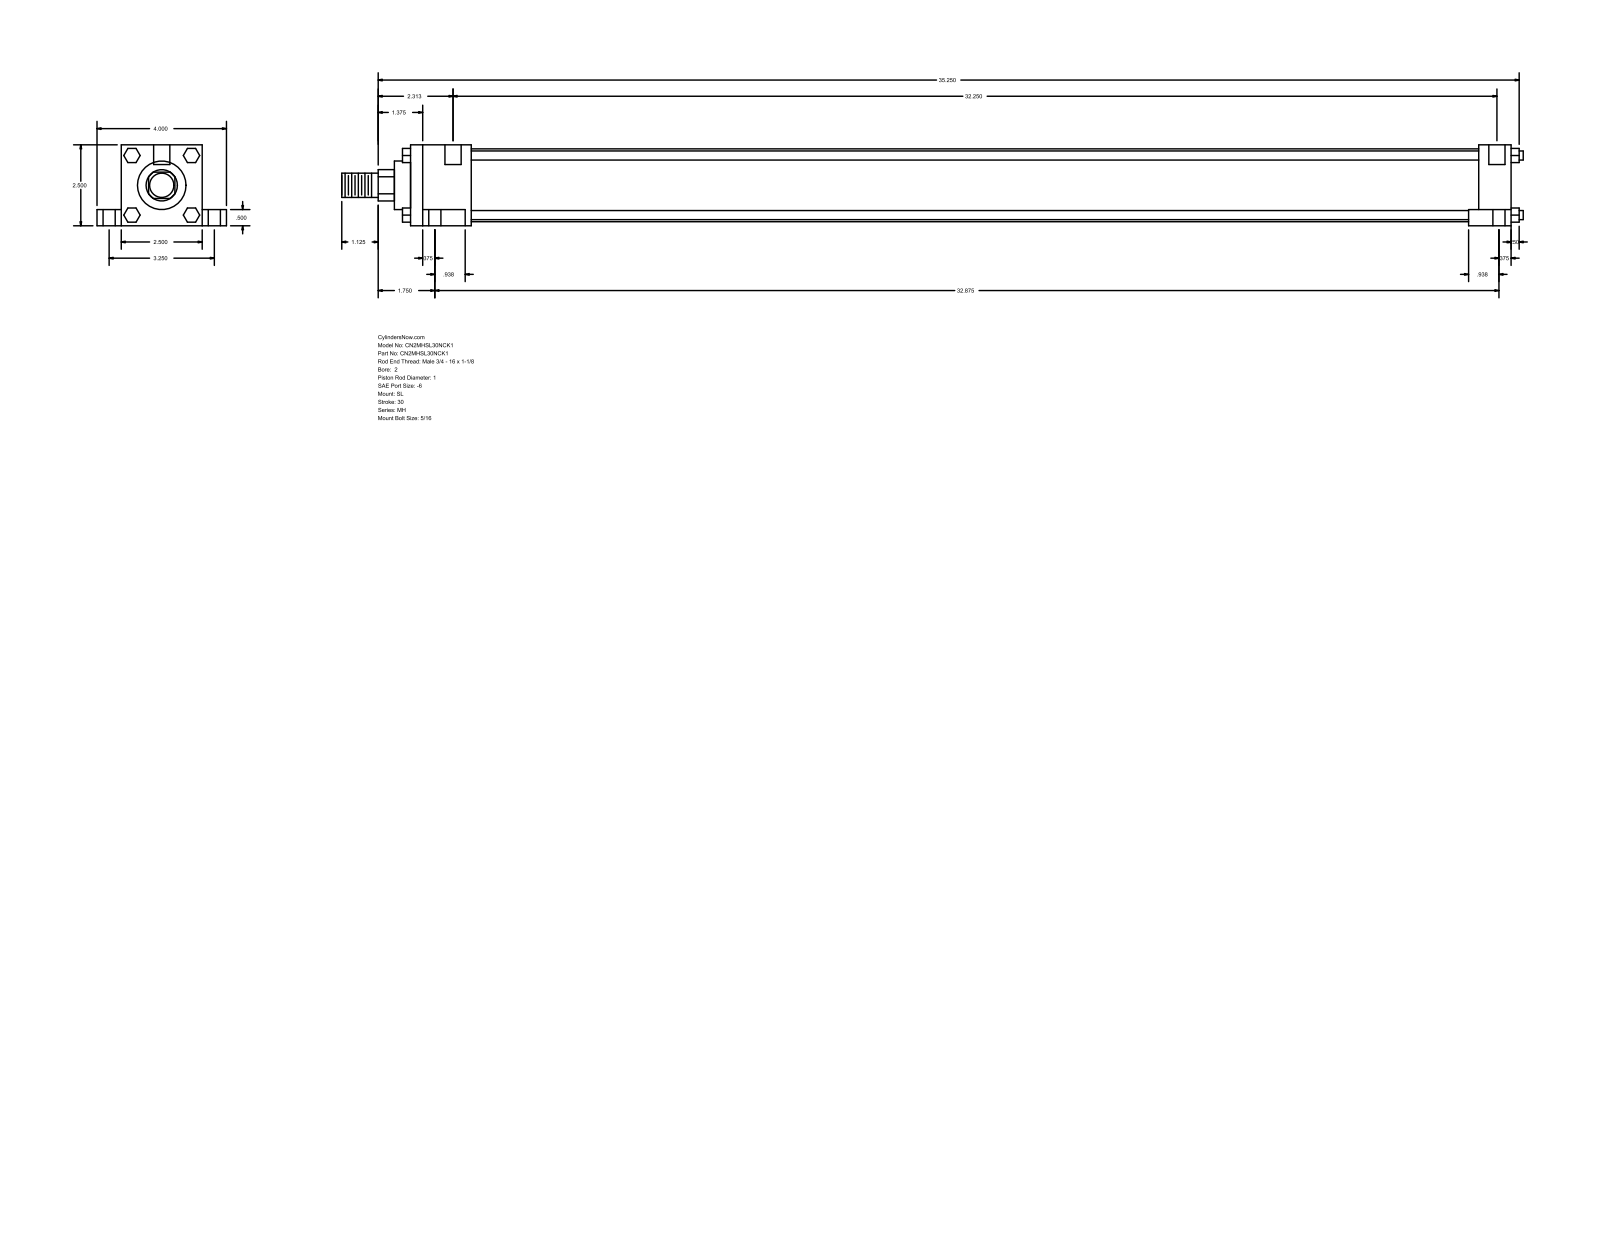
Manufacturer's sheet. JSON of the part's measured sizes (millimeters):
{"part_name": "MH_SL__0200_1", "step_written_by": "GSSL Pune (CONFIG_CONTROL_DESIGN)", "units": "millimeters", "bodies": {"solids": 0, "faces": 148, "planar": 112, "cylindrical": 36, "other": 0}, "overall_size": [927.1, 101.6, 63.5], "round_holes": [[5.56, 4], [9.53, 4], [15.88, 4], [12.7, 2]], "round_bosses_or_shafts": [[7.14, 4], [57.15, 1], [38.1, 1], [25.4, 1], [19.05, 1]], "partial_cylinders_radius": [[12.29, 1]], "face_to_face_distances": [63.5, 863.6, 12.7, 19.05, 50.8, 82.55, 25.4, 838.2, 47.63, 790.57], "hole_center_spacings": [41.3, 42.36, 43.67, 82.54, 821.78, 826.53, 827.08, 834.46]}
